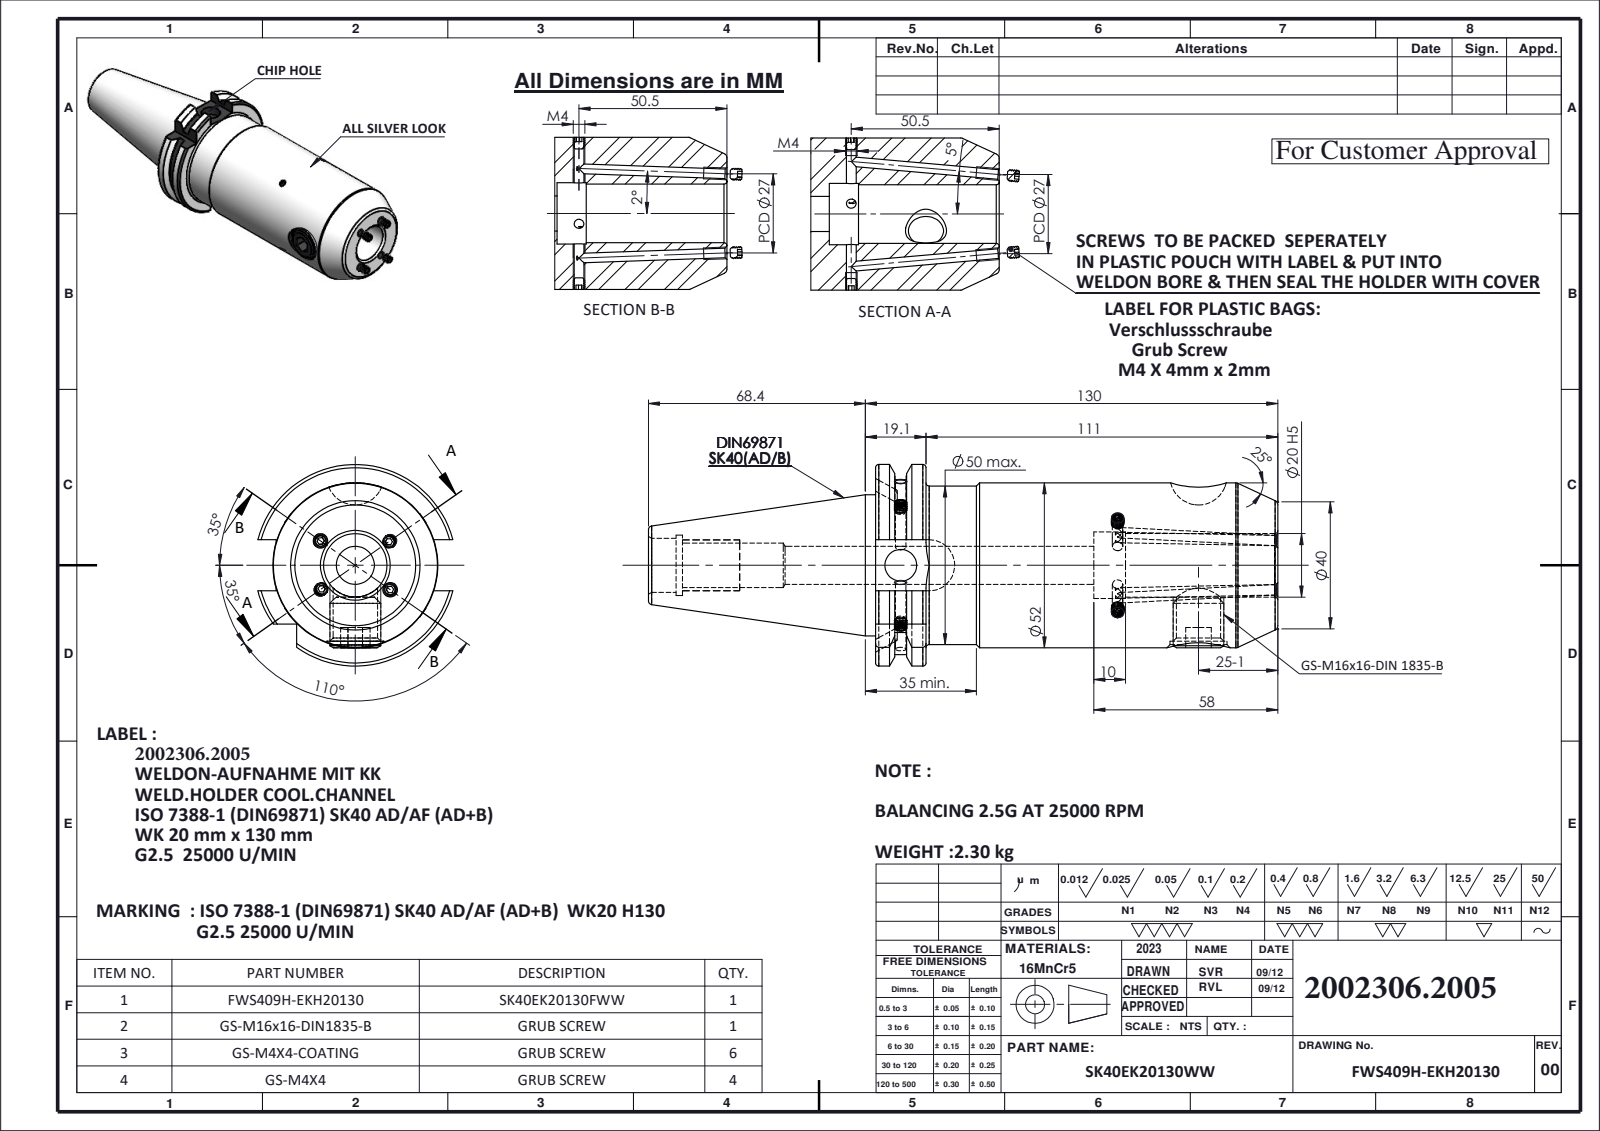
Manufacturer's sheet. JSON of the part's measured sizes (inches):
{"part_name": "GS-M4X4_DIN 913 - M4 x 4-N; SK40EK20130FWW; GS-M4X4-COATING_DIN 913 - M4 x 4-N; GS-M16X16-DIN1835-B_ISO 4026 - M16 x 10-N (+1 more)", "step_written_by": "SolidWorks 2023 (CONFIG_CONTROL_DESIGN)", "units": "inches", "bodies": {"solids": 12, "faces": 646, "planar": 131, "cylindrical": 172, "other": 343}, "overall_size": [8.085, 2.502, 2.42], "volume_in3": 18.29, "surface_area_in2": 76.56, "round_holes": [[0.13, 9], [0.551, 2], [0.394, 1], [0.472, 1], [0.669, 1], [0.709, 1], [0.748, 1], [0.787, 1], [0.827, 1]], "round_bosses_or_shafts": [[0.157, 10], [2.047, 1], [1.969, 1], [1.75, 1], [0.63, 1]], "partial_cylinders_radius": [[0.317, 1], [1.107, 1], [1.251, 1]], "face_to_face_distances": [4.992, 0.626, 4.366, 2.709, 2.083, 2.283, 1.882, 0.634, 2.819, 3.445]}
